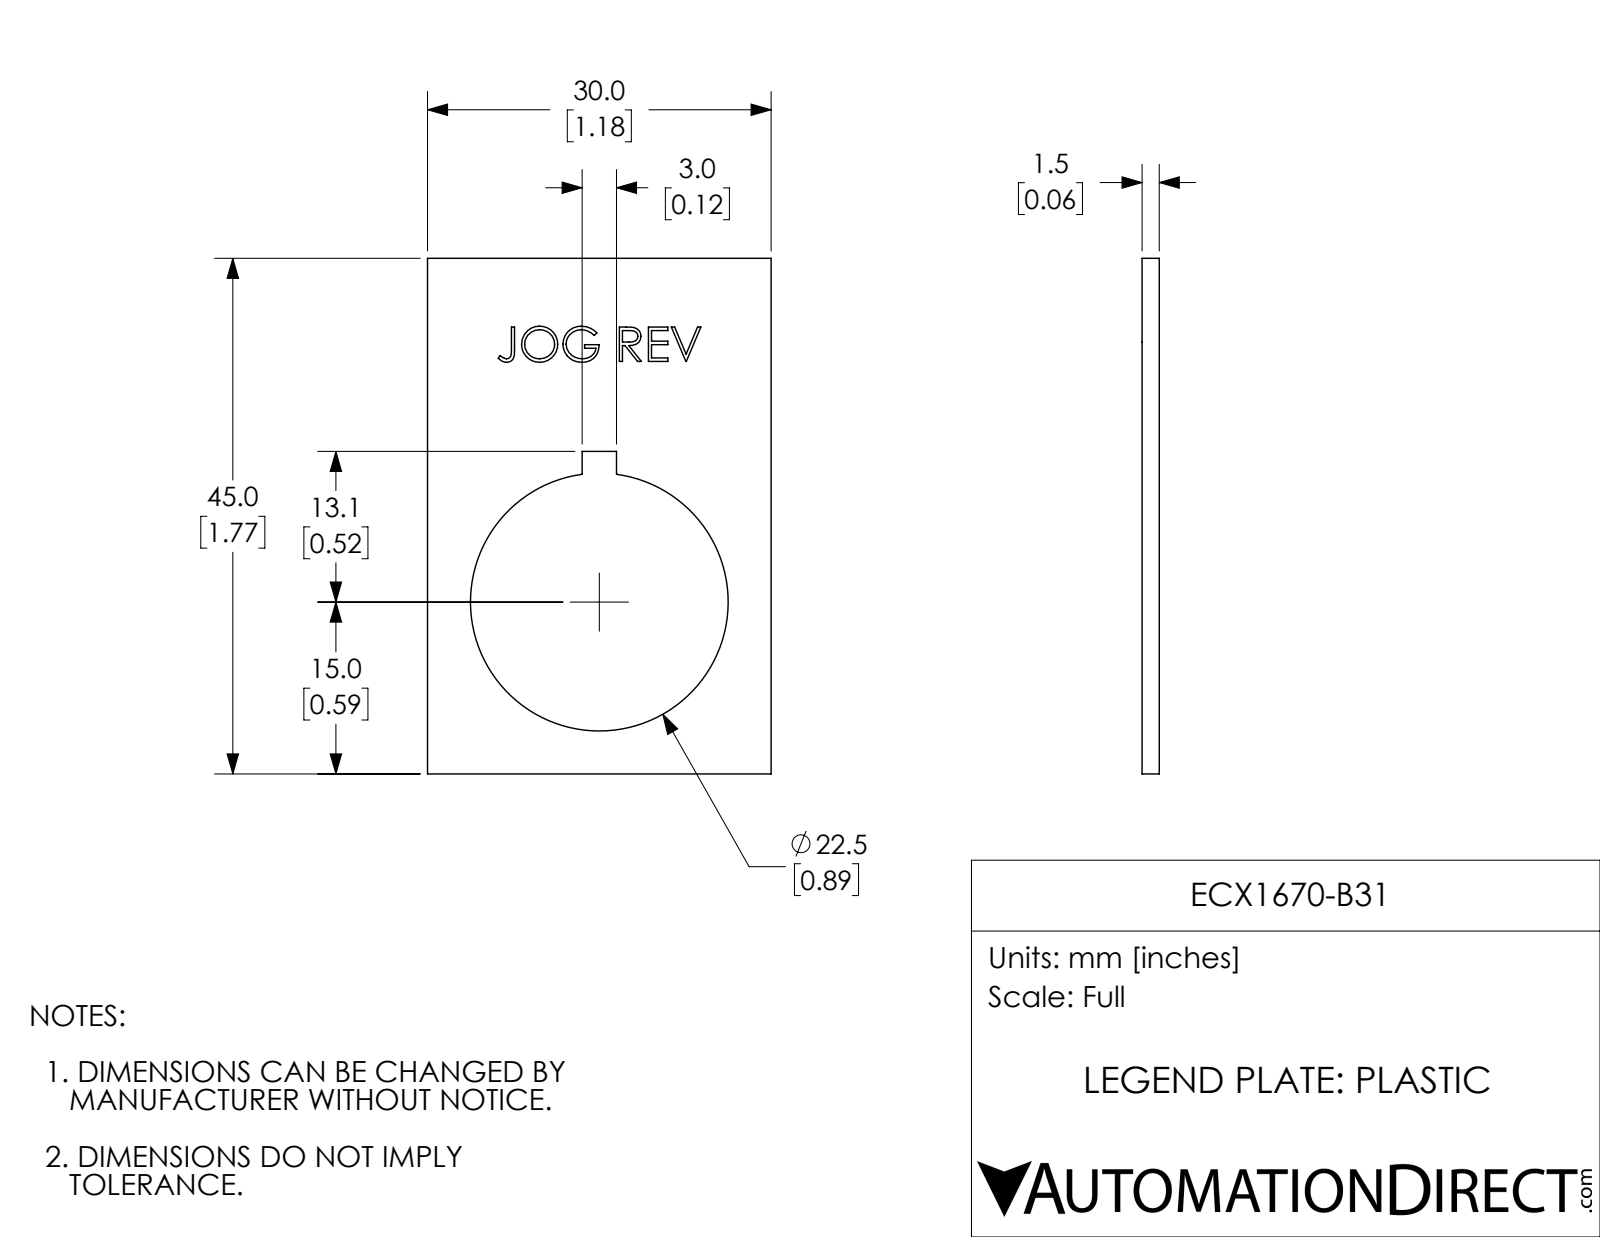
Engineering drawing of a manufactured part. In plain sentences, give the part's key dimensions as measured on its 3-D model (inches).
The part is named "ECX1670-B31". Its 3-D file was written by "SolidWorks 2017 (AUTOMOTIVE_DESIGN)". It is 1 solid with 85 faces: 55 planar, 3 cylindrical and 27 other. Overall it measures 1.772 by 1.181 by 0.059 inches. Its volume is 0.087 cubic inches and its surface area 3.46 square inches. Round holes: 1 of diameter 0.886. The main face-to-face distances are 0.059, 1.181, 1.772, 0.058, 0.531, 0.65, 1.108, 0.663, 0.118, 0.012.
